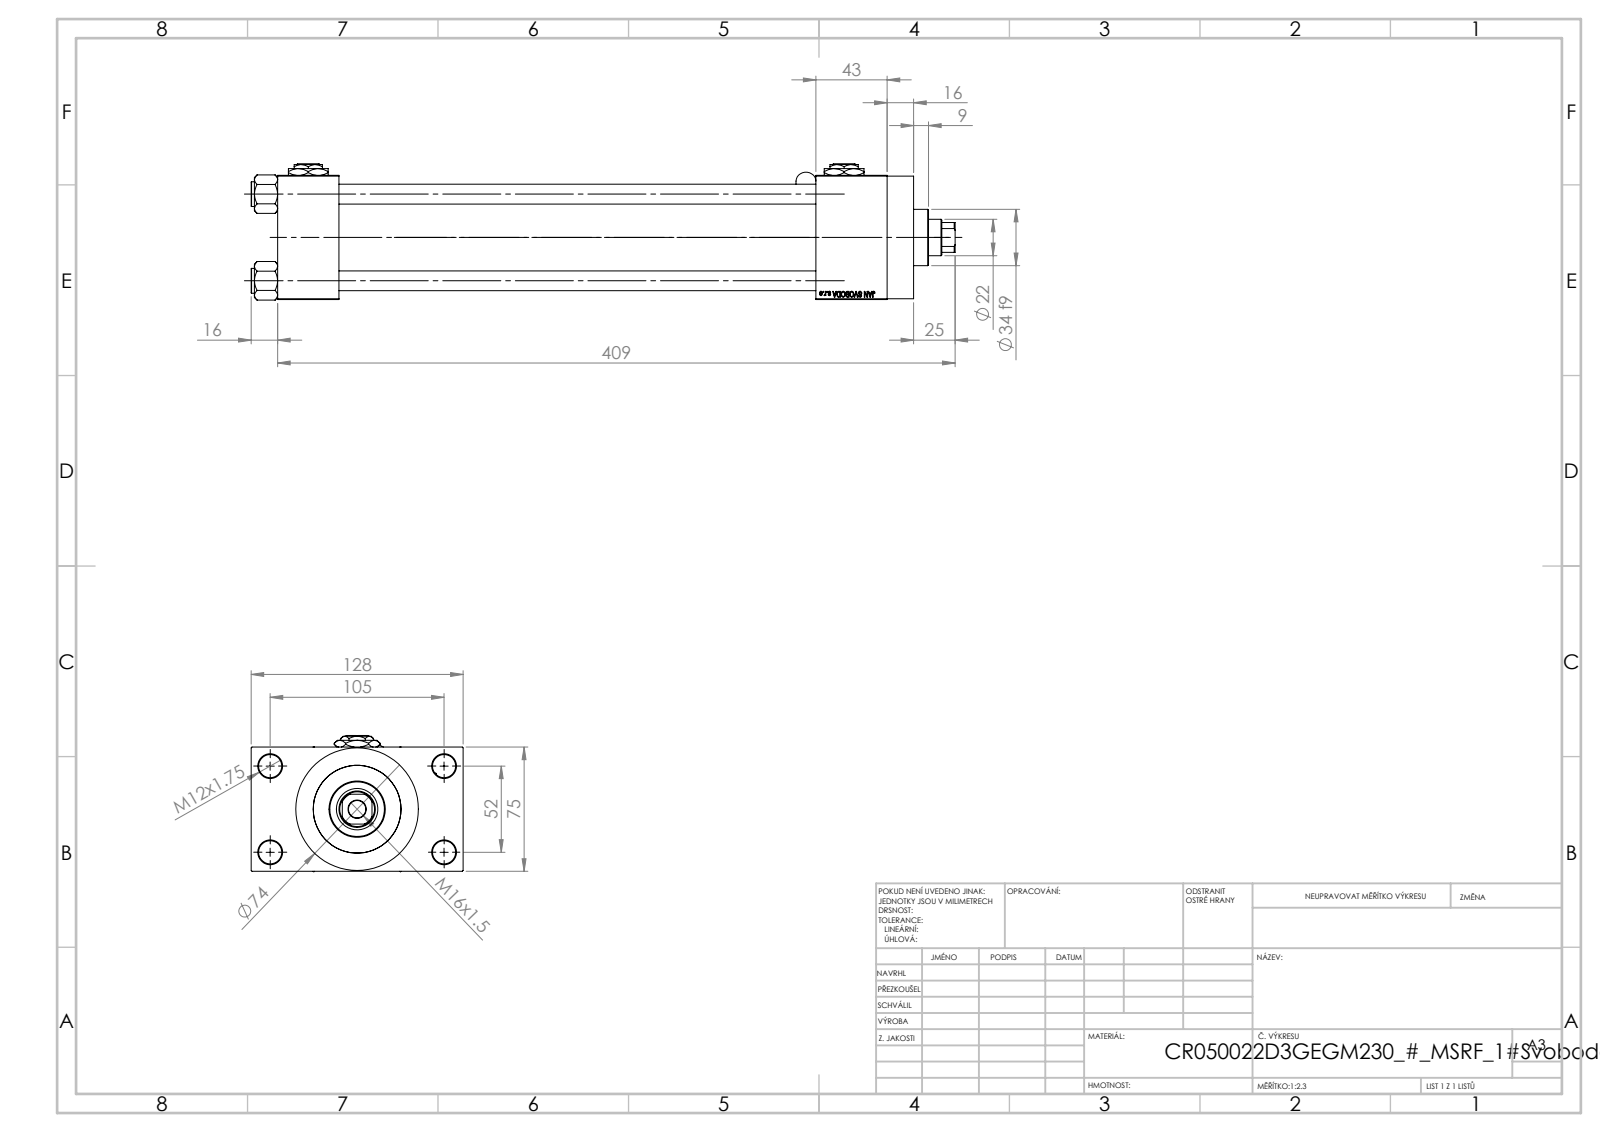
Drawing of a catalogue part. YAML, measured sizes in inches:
part_name: "V215_VC_A; V215CR_D_Body; NUT_M5_D; MSRF_MSRG1 (+3 more)"
step_written_by: "SolidWorks 2019 (CONFIG_CONTROL_DESIGN)"
units: inches
bodies: {solids: 14, faces: 1237, planar: 563, cylindrical: 114, other: 560}
overall_size: [16.732, 5.039, 3.239]
volume: 67.86
surface_area: 462.8
round_holes:
  - {diameter: 0.472, count: 4}
  - {diameter: 0.551, count: 4}
  - {diameter: 0.276, count: 2}
  - {diameter: 0.825, count: 2}
  - {diameter: 1.181, count: 2}
  - {diameter: 0.413, count: 1}
  - {diameter: 0.866, count: 1}
  - {diameter: 0.984, count: 1}
  - {diameter: 1.614, count: 1}
  - {diameter: 1.969, count: 1}
  - {diameter: 2.087, count: 1}
round_bosses_or_shafts:
  - {diameter: 0.591, count: 4}
  - {diameter: 2.913, count: 1}
  - {diameter: 2.205, count: 1}
  - {diameter: 1.339, count: 1}
  - {diameter: 0.197, count: 1}
  - {diameter: 0.098, count: 1}
partial_cylinders:
  - {radius: 0.02, count: 6}
  - {radius: 0.236, count: 2}
  - {radius: 0.413, count: 1}
face_to_face_distances: [2.953, 11.339, 1.457, 12.795, 1.043, 3.996, 14.488, 13.031, 1.693, 0.63]
hole_center_spacings: [1.037, 1.456, 2.059, 2.3, 2.307, 3.096, 3.715, 2.047]
